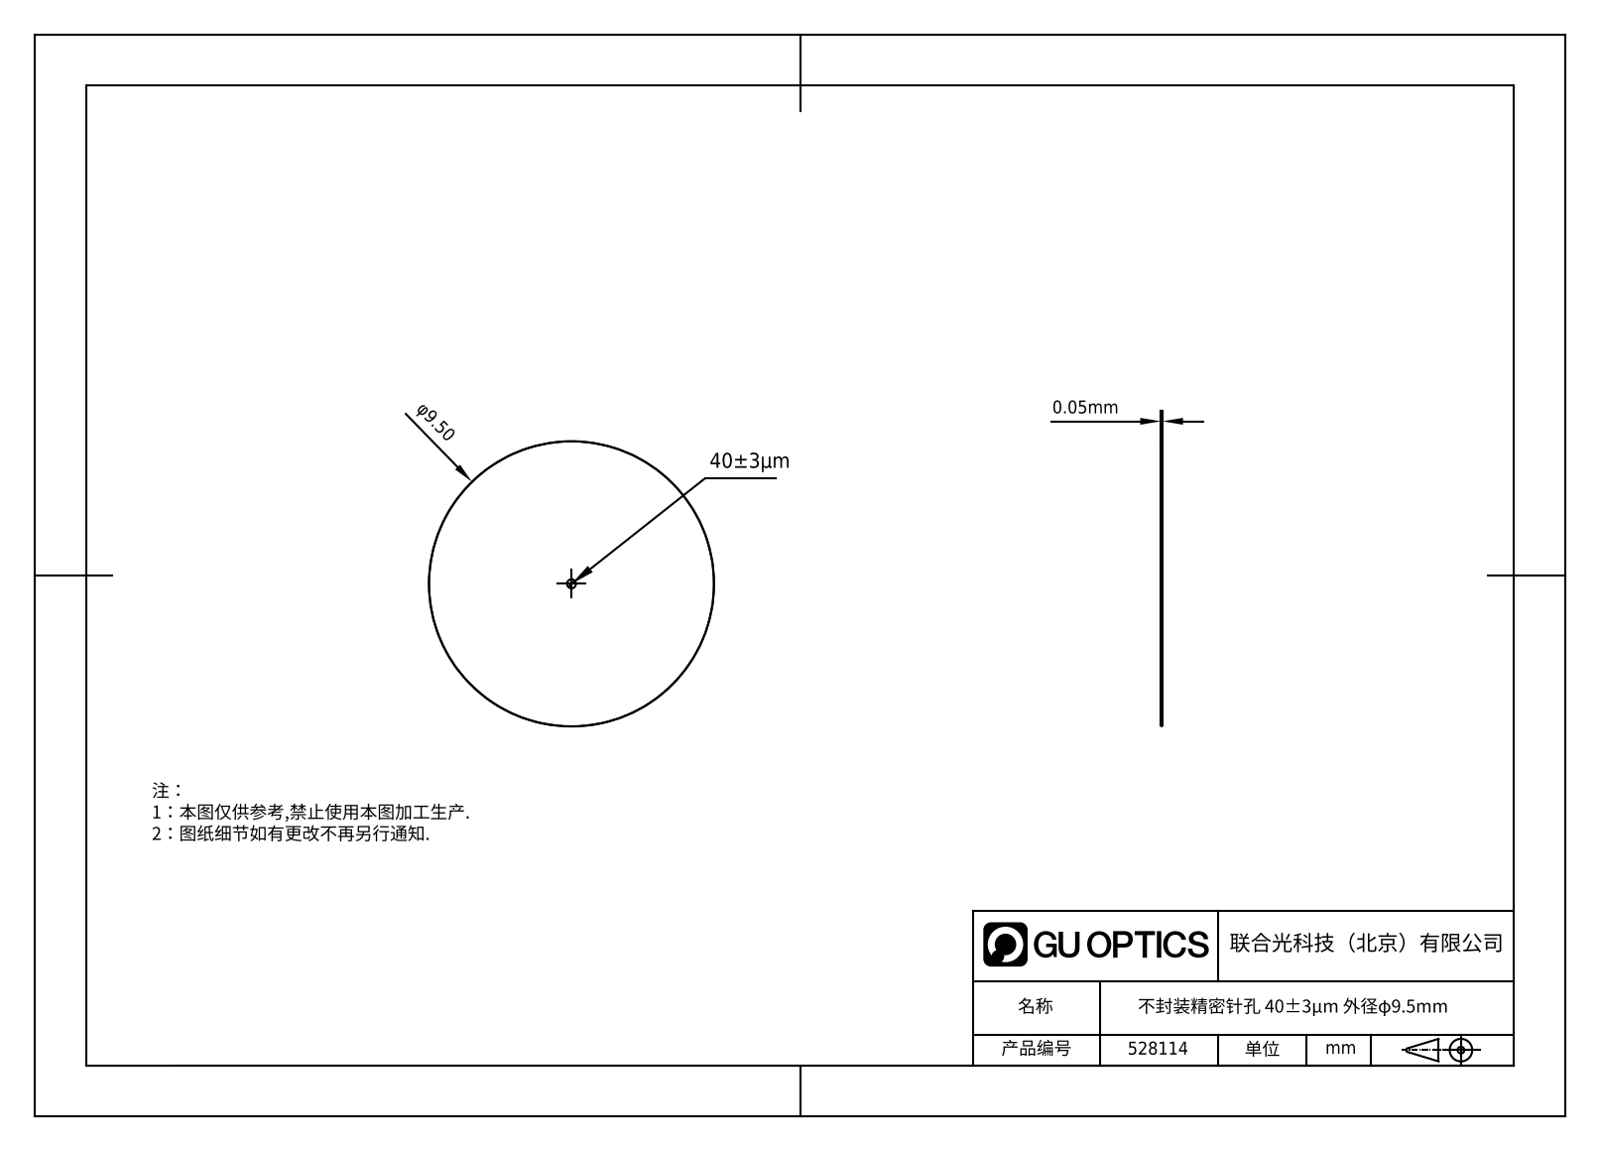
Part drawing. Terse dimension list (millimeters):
name: 1.5.3.7-ZXO-9.5-40
written by: SolidWorks 2021 (CONFIG_CONTROL_DESIGN)
unit: mm
bodies: 1 solid, 6 faces (2 planar, 4 cylindrical, 0 other)
size: 9.5 × 9.5 × 0.05
volume: 4 mm³; area: 143 mm²
bosses: 1× ⌀9.5
